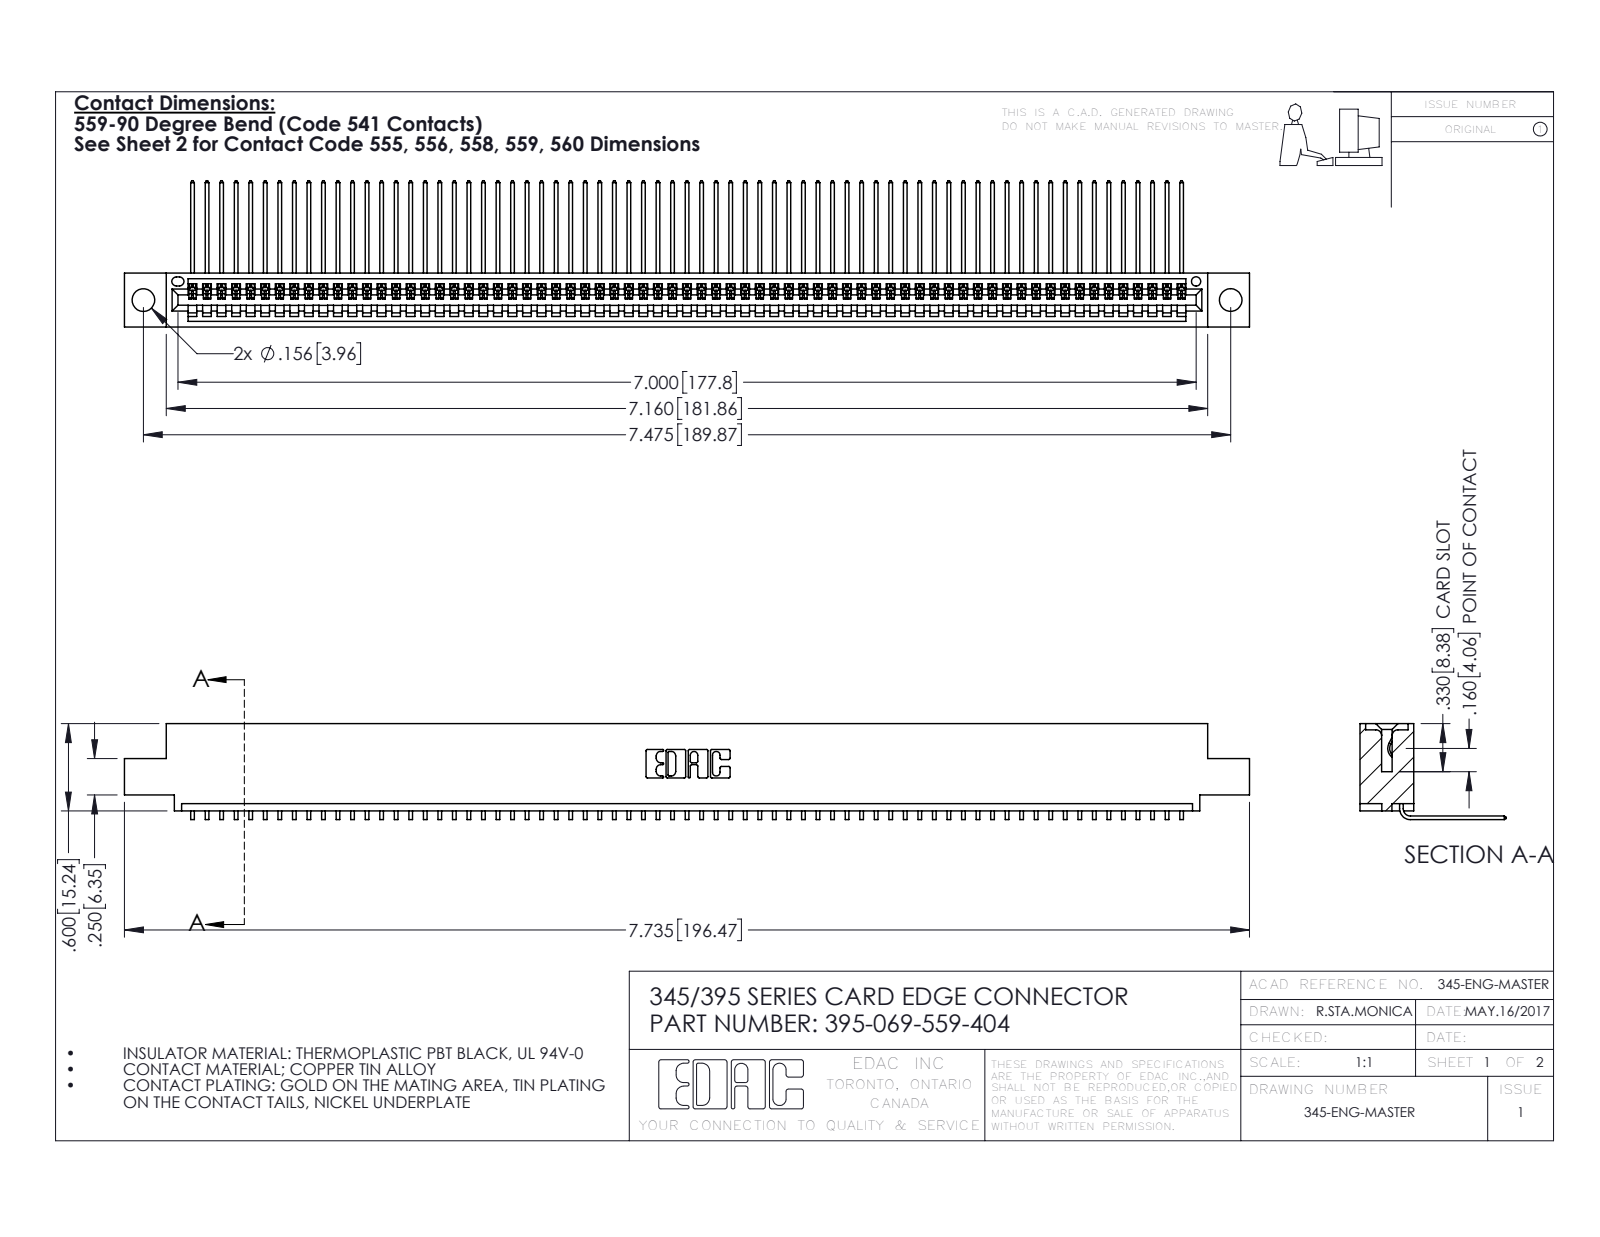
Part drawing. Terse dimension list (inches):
name: 395-069-559-404; 345-292-001_558 559 Tail - 1; 345 Part_0.110 Offset - 0.156 Dia-TH
written by: SolidWorks 2016 (CONFIG_CONTROL_DESIGN)
unit: in
bodies: 70 solids, 4270 faces (2982 planar, 1288 cylindrical, 0 other)
size: 7.735 × 1.005 × 0.659
volume: 1.156 in³; area: 41.53 in²
holes: 2× ⌀0.156, 1× ⌀0.064
rounds: 138× R0.006, 22× R0.01, 6× R0.007, 6× R0.031, 3× R0.026, 2× R0.031, 2× R0.04, 1× R0.014
face distances: 0.072, 0.298, 0.37, 0.2, 0.098, 0.272, 0.025, 0.225, 0.149, 0.072
hole spacings: 0.27, 7.239, 7.475
